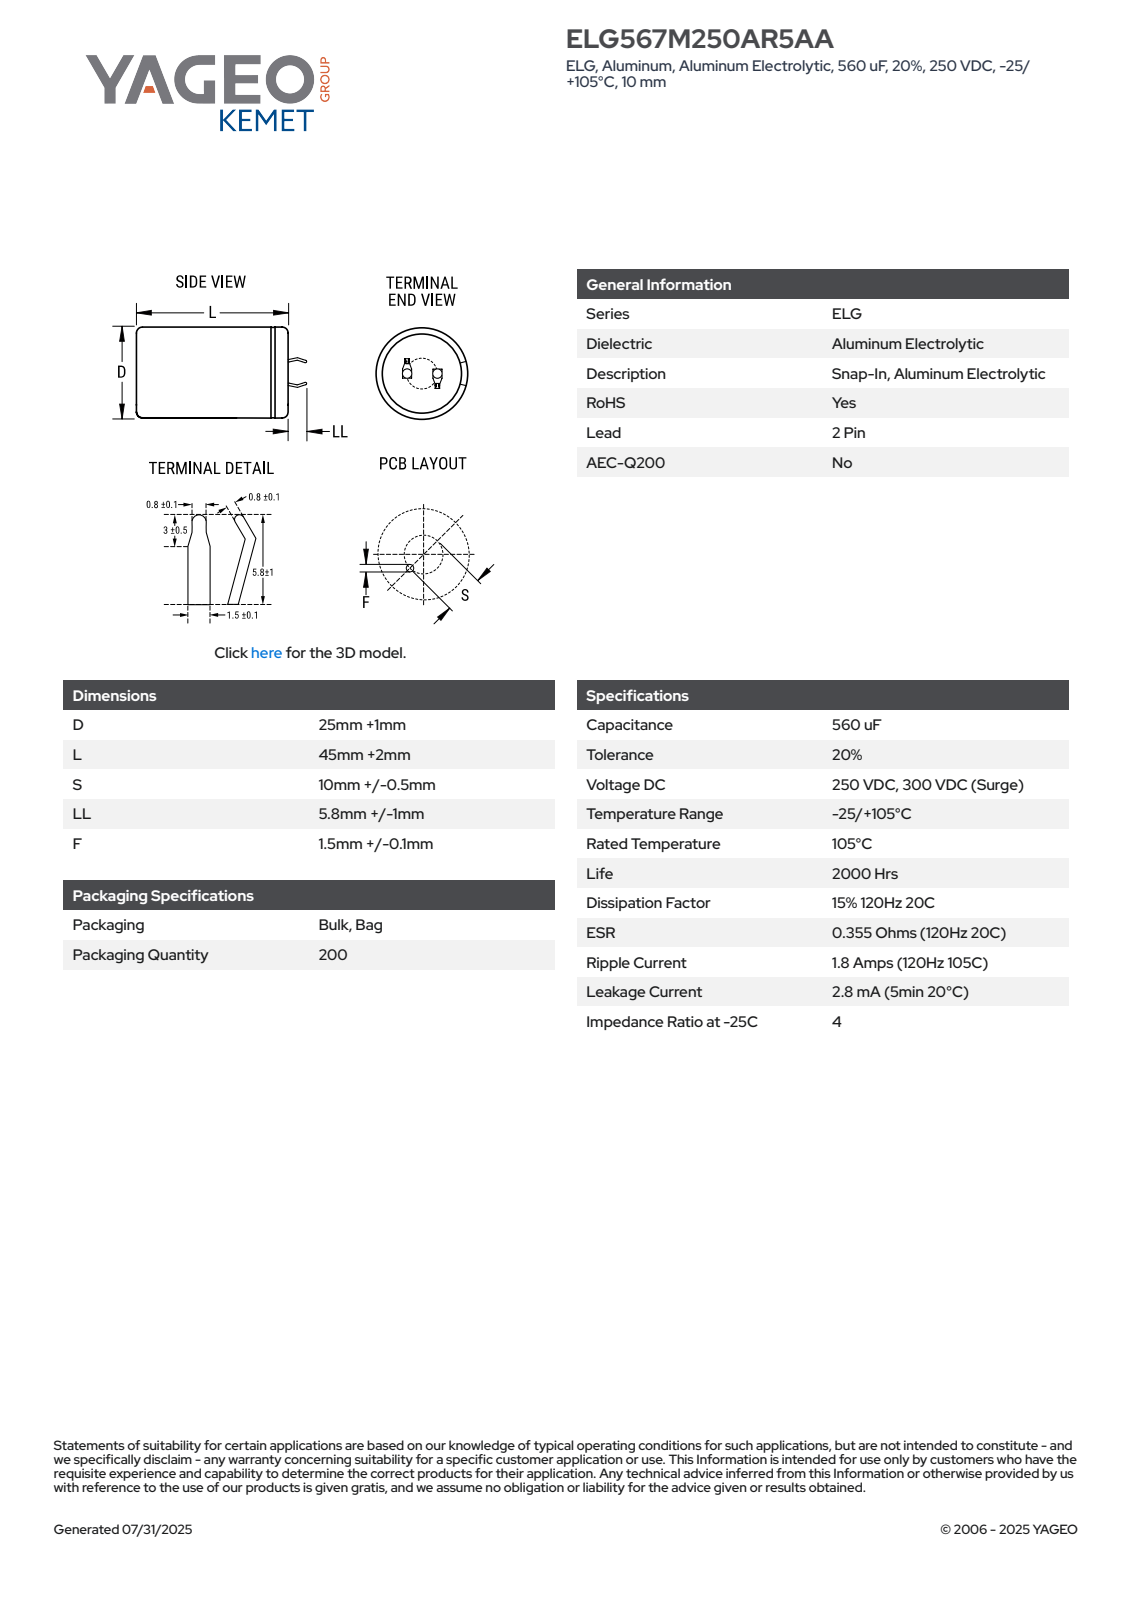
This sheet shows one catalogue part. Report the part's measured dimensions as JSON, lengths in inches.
{"part_name": "CARS_K2P_25X45_D26L47S10LL6.8F1.6", "step_written_by": "SolidWorks 2014 (AUTOMOTIVE_DESIGN)", "units": "inches", "bodies": {"solids": 1, "faces": 100, "planar": 52, "cylindrical": 9, "other": 39}, "overall_size": [2.118, 1.024, 1.024], "volume_in3": 1.511, "surface_area_in2": 7.626, "round_holes": [[0.906, 1]], "round_bosses_or_shafts": [[1.024, 1]], "partial_cylinders_radius": [[0.511, 1]], "face_to_face_distances": [1.85, 1.87, 0.02, 0.024, 0.279, 0.03, 0.053, 0.302, 0.255, 0.023]}
